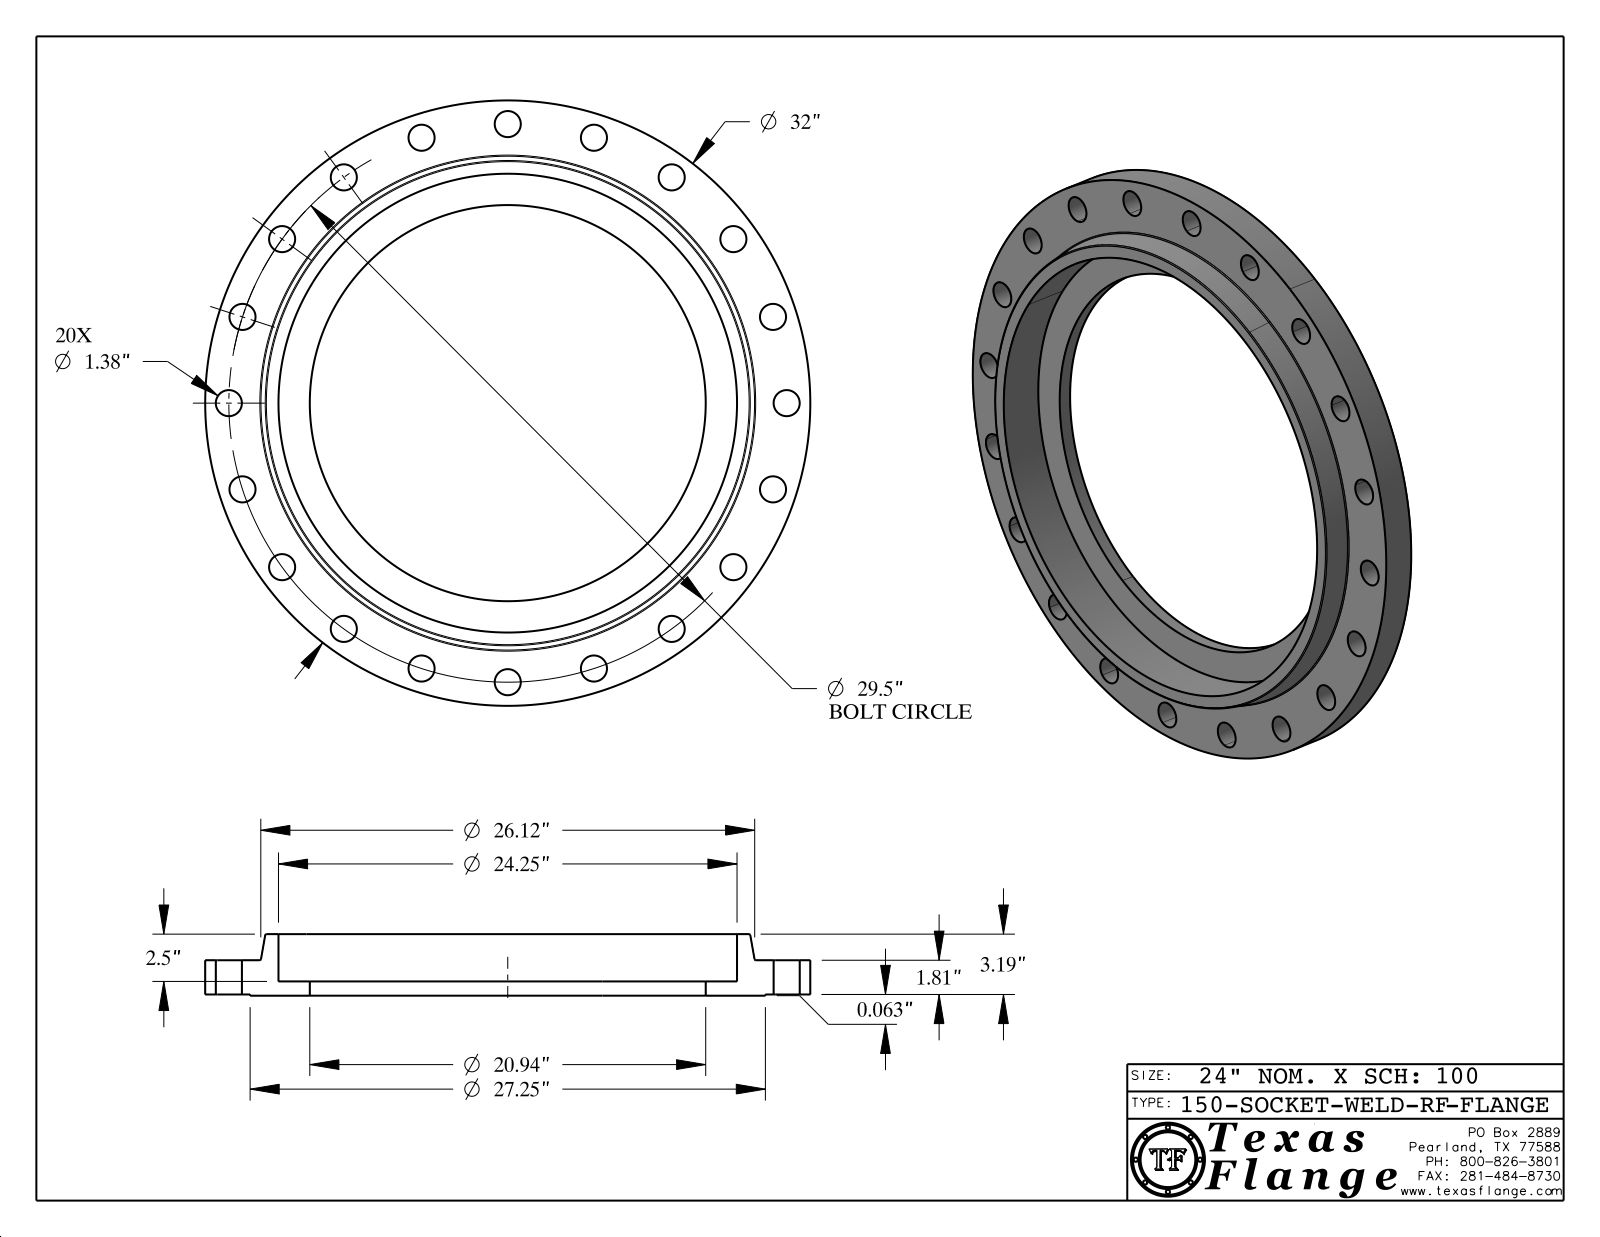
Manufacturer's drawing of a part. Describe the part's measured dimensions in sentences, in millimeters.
The part is named "150-SOCKET-WELD-RF". Its 3-D file was written by "CATIA V5 STEP AP214 (AUTOMOTIVE_DESIGN)". It is 1 solid with 444 faces: 370 planar, 68 cylindrical and 6 other. Overall it measures 812.8 by 812.8 by 82.6 millimeters. Its volume is 12 290 000 cubic millimeters and its surface area 991 000 square millimeters. Round holes: 20 of diameter 35.1, 1 of diameter 12.6, 1 of diameter 531.8, 1 of diameter 616. Round bosses or shafts: 8 of diameter 0.8, 1 of diameter 812.8, 1 of diameter 692.2, 1 of diameter 9.9. The main face-to-face distances are 47.5, 1.6, 46, 19.1, 17.5, 28.4, 82.6, 81, 63.5, 35.1. The hole center spacings are 374.7, 740.1, 117.2, 440.4, 529.8, 606.2, 667.6, 231.5.
